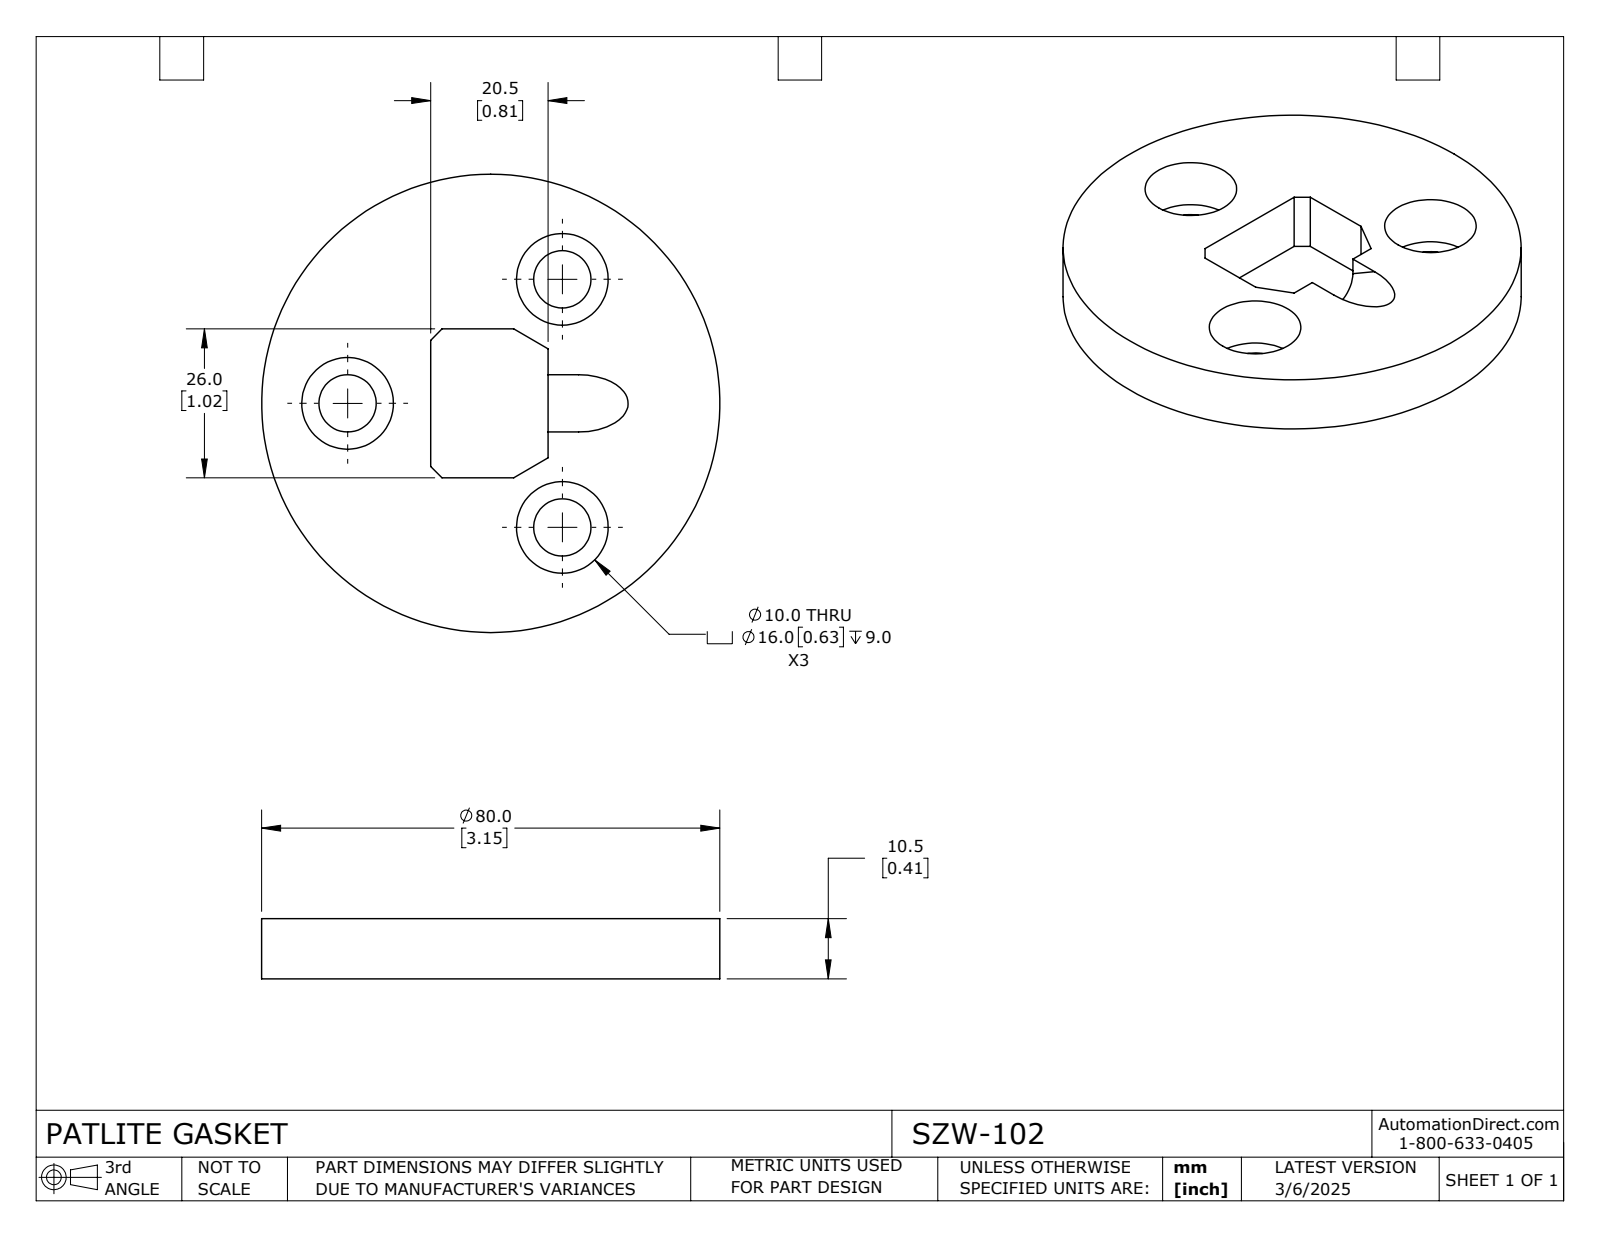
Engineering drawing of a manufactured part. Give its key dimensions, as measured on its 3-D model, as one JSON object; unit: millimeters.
{"part_name": "SZW-102", "step_written_by": "SolidWorks 2024 (CONFIG_CONTROL_DESIGN)", "units": "millimeters", "bodies": {"solids": 1, "faces": 30, "planar": 15, "cylindrical": 14, "other": 1}, "overall_size": [80, 80, 10.5], "volume_mm3": 41226, "surface_area_mm2": 13613, "round_holes": [[10, 3], [16, 3]], "round_bosses_or_shafts": [[80, 1]], "face_to_face_distances": [10.5, 1.5, 9, 26, 20.5, 8, 18, 10], "hole_center_spacings": [43.3]}
